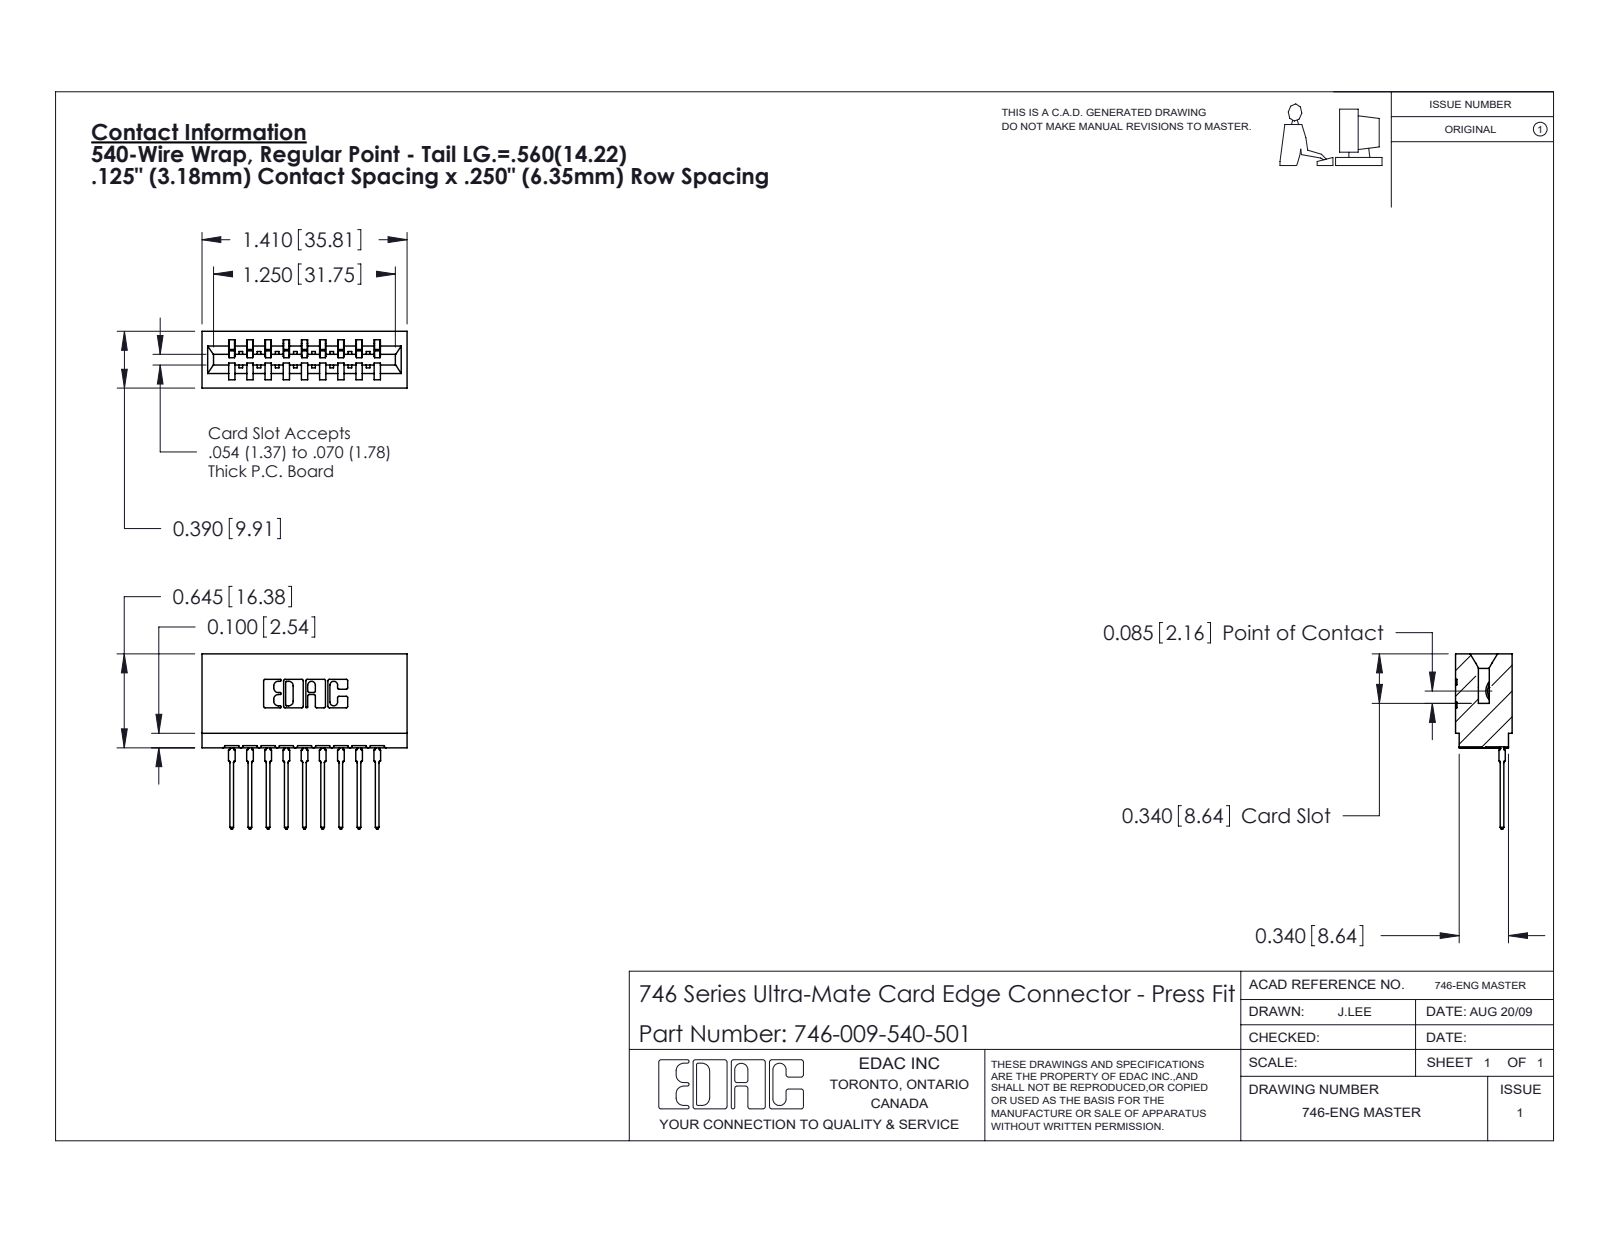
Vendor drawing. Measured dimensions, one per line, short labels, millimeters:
name: 746 Part_.340 Slot Depth - 01; 746-009-540-501; 746-292-001_540
written by: SolidWorks 2020 (CONFIG_CONTROL_DESIGN)
unit: mm
bodies: 10 solids, 1069 faces (622 planar, 213 cylindrical, 234 other)
size: 35.8 × 30.6 × 9.9
volume: 4 240 mm³; area: 5 330 mm²
rounds: 22× R0.3, 18× R0.5, 10× R0.4, 6× R0.2, 6× R0.8, 4× R0.1, 4× R0.3, 3× R0.7
face distances: 6.4, 12.7, 1.1, 8.5, 3.2, 3.2, 1.4, 7.4, 5.3, 9.5
